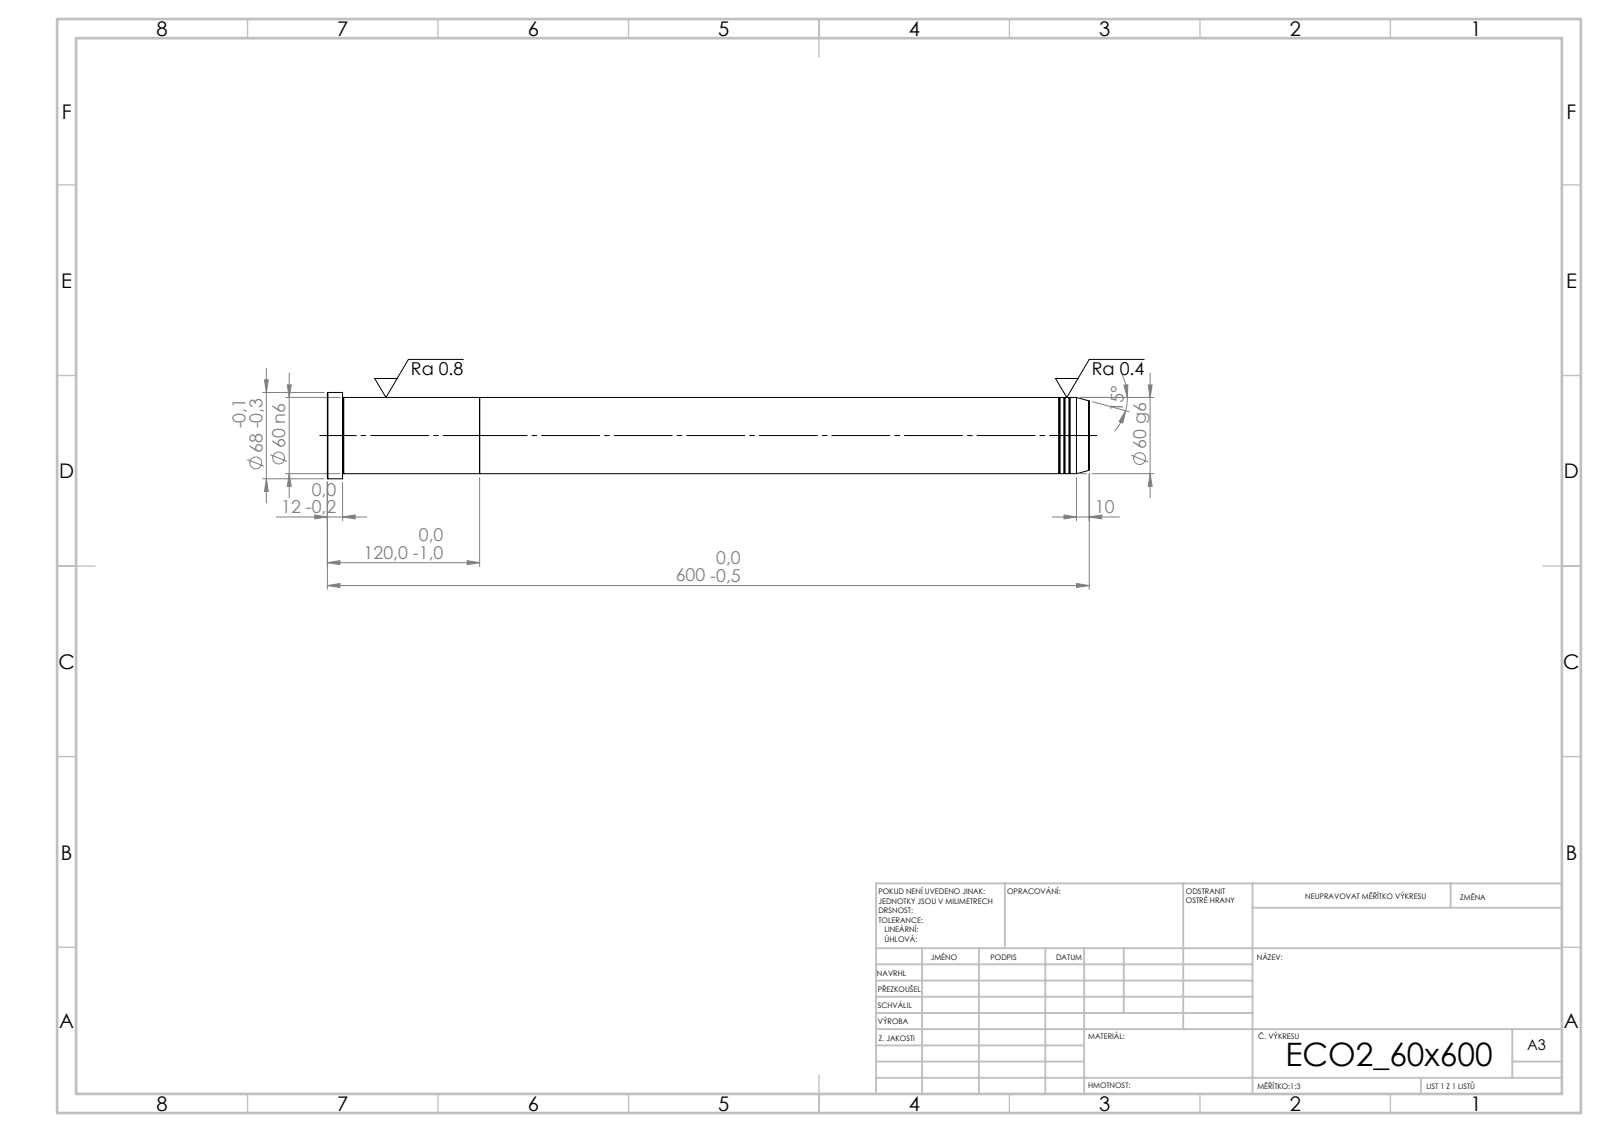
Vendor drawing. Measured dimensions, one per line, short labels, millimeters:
written by: SolidWorks 2019 (CONFIG_CONTROL_DESIGN)
unit: mm
bodies: 2 solids, 39 faces (5 planar, 12 cylindrical, 22 other)
size: 600 × 68 × 68
volume: 1 703 000 mm³; area: 126 149 mm²
bosses: 1× ⌀68, 1× ⌀60
face distances: 120, 480, 600, 588, 108, 12
